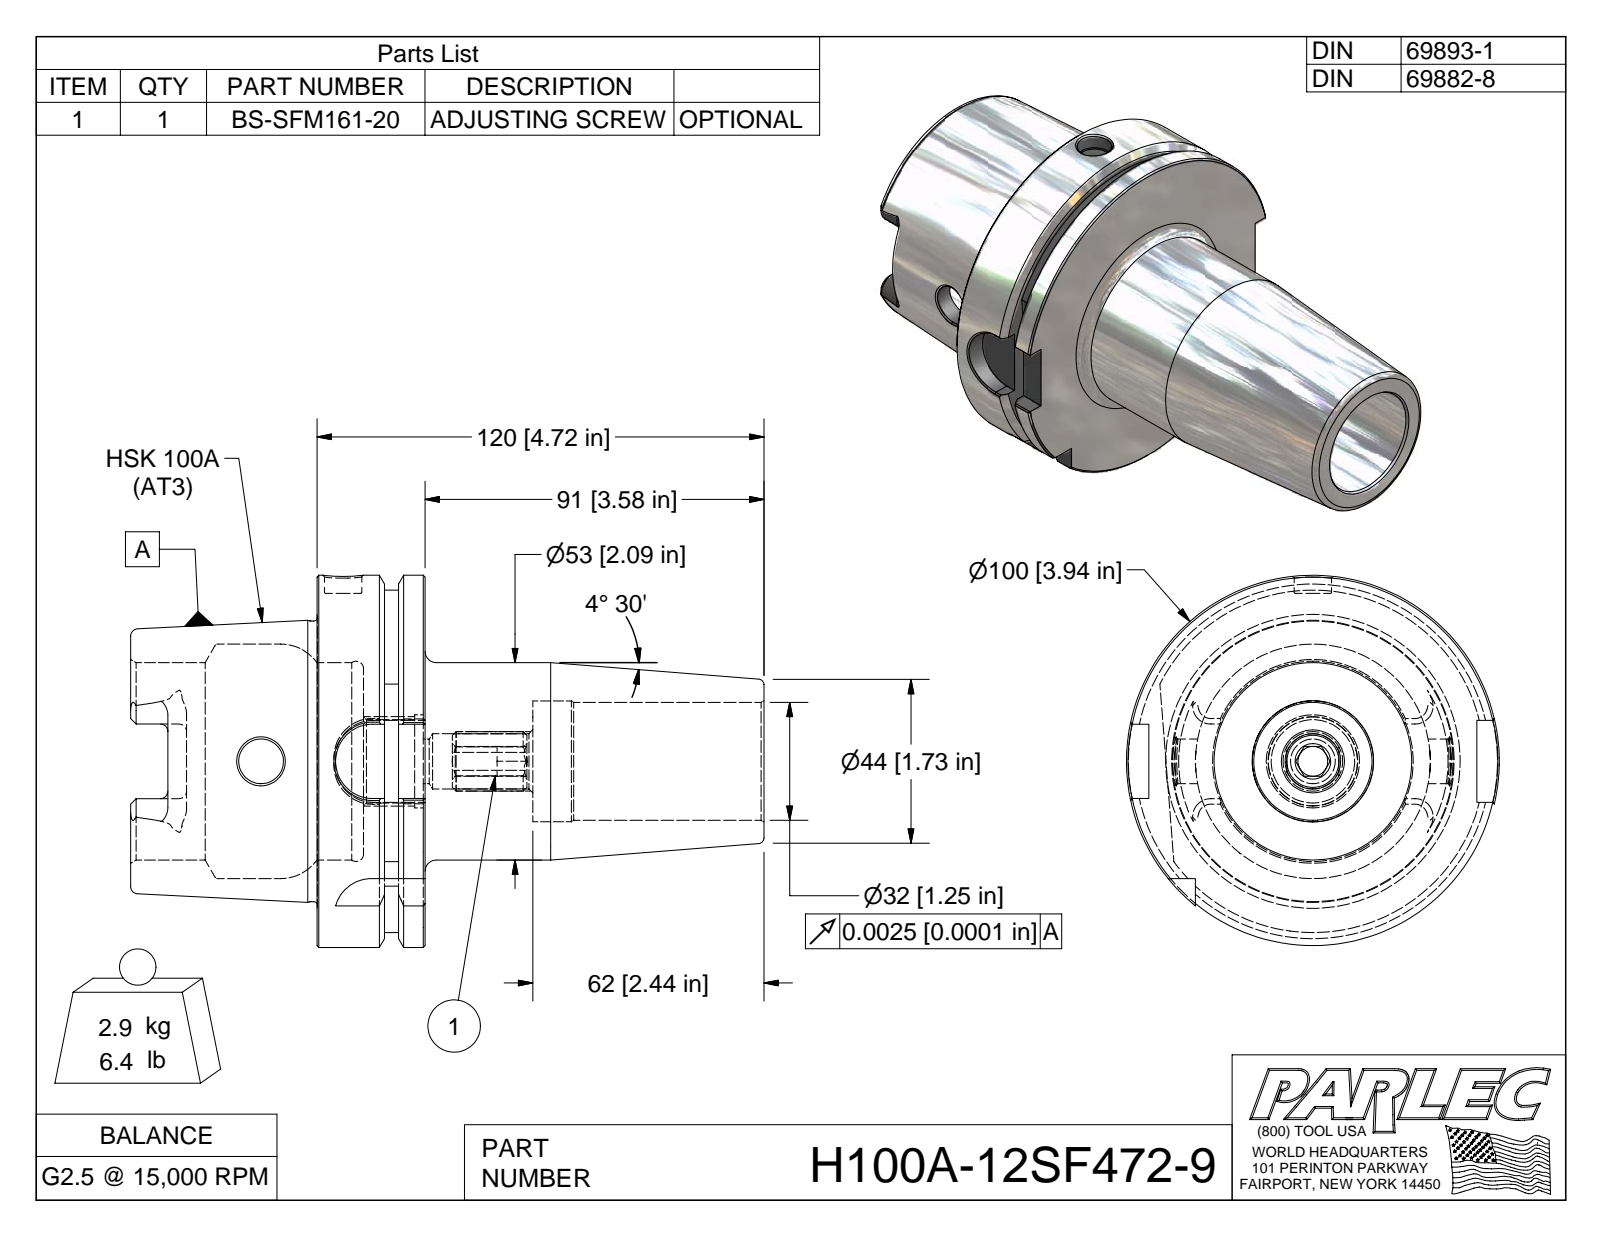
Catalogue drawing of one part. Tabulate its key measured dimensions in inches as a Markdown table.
| quantity | value |
| --- | --- |
| part name | H100A-12SF472-9; H100A-12SF472-9-1; BS-SFM161-20 |
| STEP written by | Autodesk Inventor 2012 (AUTOMOTIVE_DESIGN) |
| units | inches |
| bodies | 2 solids, 149 faces (54 planar, 38 cylindrical, 57 other) |
| overall size | 6.689 × 3.937 × 3.937 |
| volume | 23.35 in³ |
| surface area | 112.3 in² |
| round holes (diameter × count) | 0.315 × 1, 0.394 × 1, 0.472 × 1, 0.472 × 1, 0.587 × 1, 0.881 × 1, 0.985 × 1, 1.248 × 1, 1.278 × 1, 2.087 × 1, 2.48 × 1 |
| round bosses / shafts (diameter × count) | 3.937 × 1, 2.967 × 1 |
| partial cylindrical surfaces (radius × count) | 0.079 × 6, 0.192 × 4, 0.394 × 4, 0.315 × 1, 1.811 × 1 |
| main face-to-face distances | 1.142, 0.492, 0.65, 1.969, 2.461, 3.11, 4.248, 2.279, 1.787, 1.137 |
